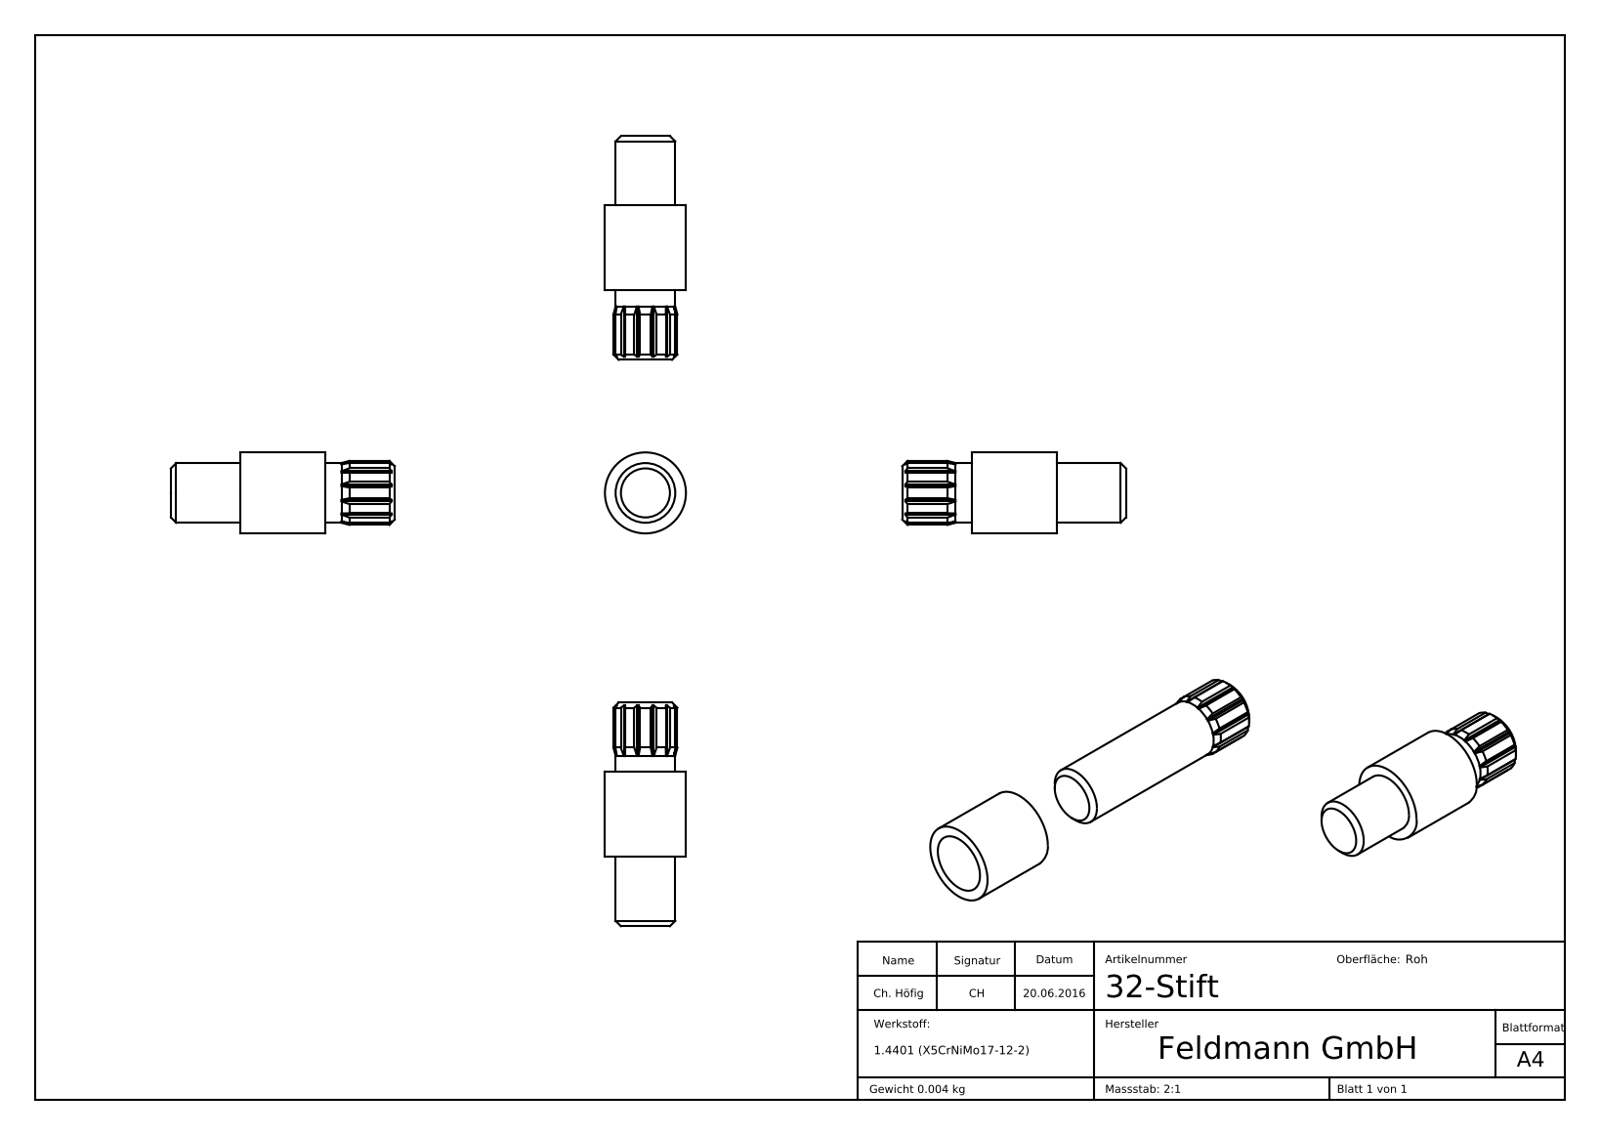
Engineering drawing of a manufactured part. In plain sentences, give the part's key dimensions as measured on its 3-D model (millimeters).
The part is named "32-STIFT Teil1_32-STIFT Teil1; 32-STIFT; 32-STIFT Teil2_32-STIFT Teil2". Its 3-D file was written by "SolidWorks 2018 (CONFIG_CONTROL_DESIGN)". It is 2 solids with 258 faces: 146 planar, 15 cylindrical and 97 other. Overall it measures 21 by 7.6 by 7.6 millimeters. Its volume is 692 cubic millimeters and its surface area 801 square millimeters. Round holes: 1 of diameter 5.6. Round bosses or shafts: 1 of diameter 7.6. Partial cylindrical surfaces (rounded edges, fillets, slot ends): 1 of radius 3. The main face-to-face distances are 6.5, 14.5, 8, 21, 4.04, 4.02, 6.4, 14.4, 20.9, 1.35.
